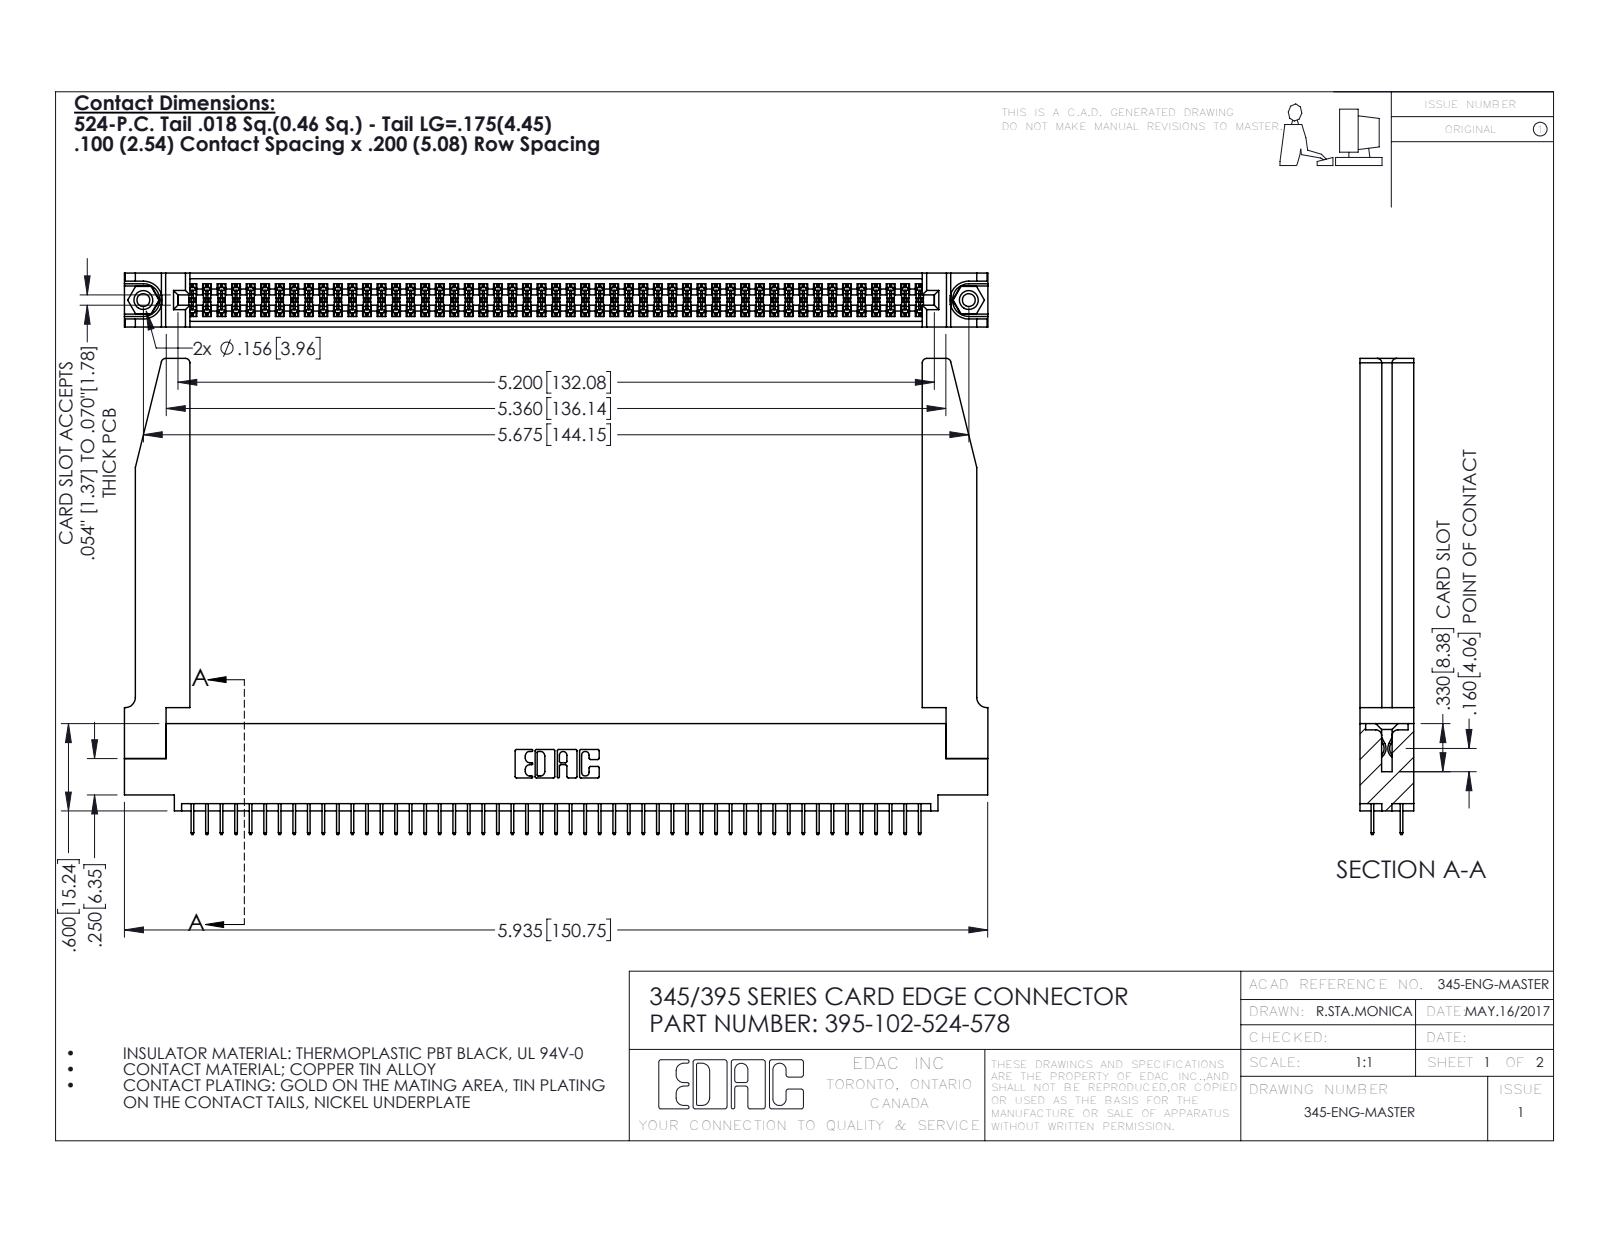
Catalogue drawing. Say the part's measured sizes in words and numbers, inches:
The part is named "395-102-524-578; 345-250-001_345-250-001-102; 345-292-001_345-293-124; 345-220-078_345-220-078 (+1 more)". Its 3-D file was written by "SolidWorks 2016 (CONFIG_CONTROL_DESIGN)". It is 107 solids with 5872 faces: 4204 planar, 1616 cylindrical and 52 other. Overall it measures 5.936 by 3.272 by 0.37 inches. Its volume is 1.359 cubic inches and its surface area 43.61 square inches. Round holes: 2 of diameter 0.089, 2 of diameter 0.125, 2 of diameter 0.156, 1 of diameter 0.064. Round bosses or shafts: 2 of diameter 0.155. Partial cylindrical surfaces (rounded edges, fillets, slot ends): 153 of radius 0.006, 22 of radius 0.01, 8 of radius 0.03, 6 of radius 0.007, 6 of radius 0.031, 3 of radius 0.026, 2 of radius 0.014, 2 of radius 0.019. The main face-to-face distances are 0.072, 0.37, 0.298, 0.2, 0.098, 0.272, 0.025, 0.225, 0.072, 0.148. The hole center spacings are 0.27, 5.439, 5.675.
